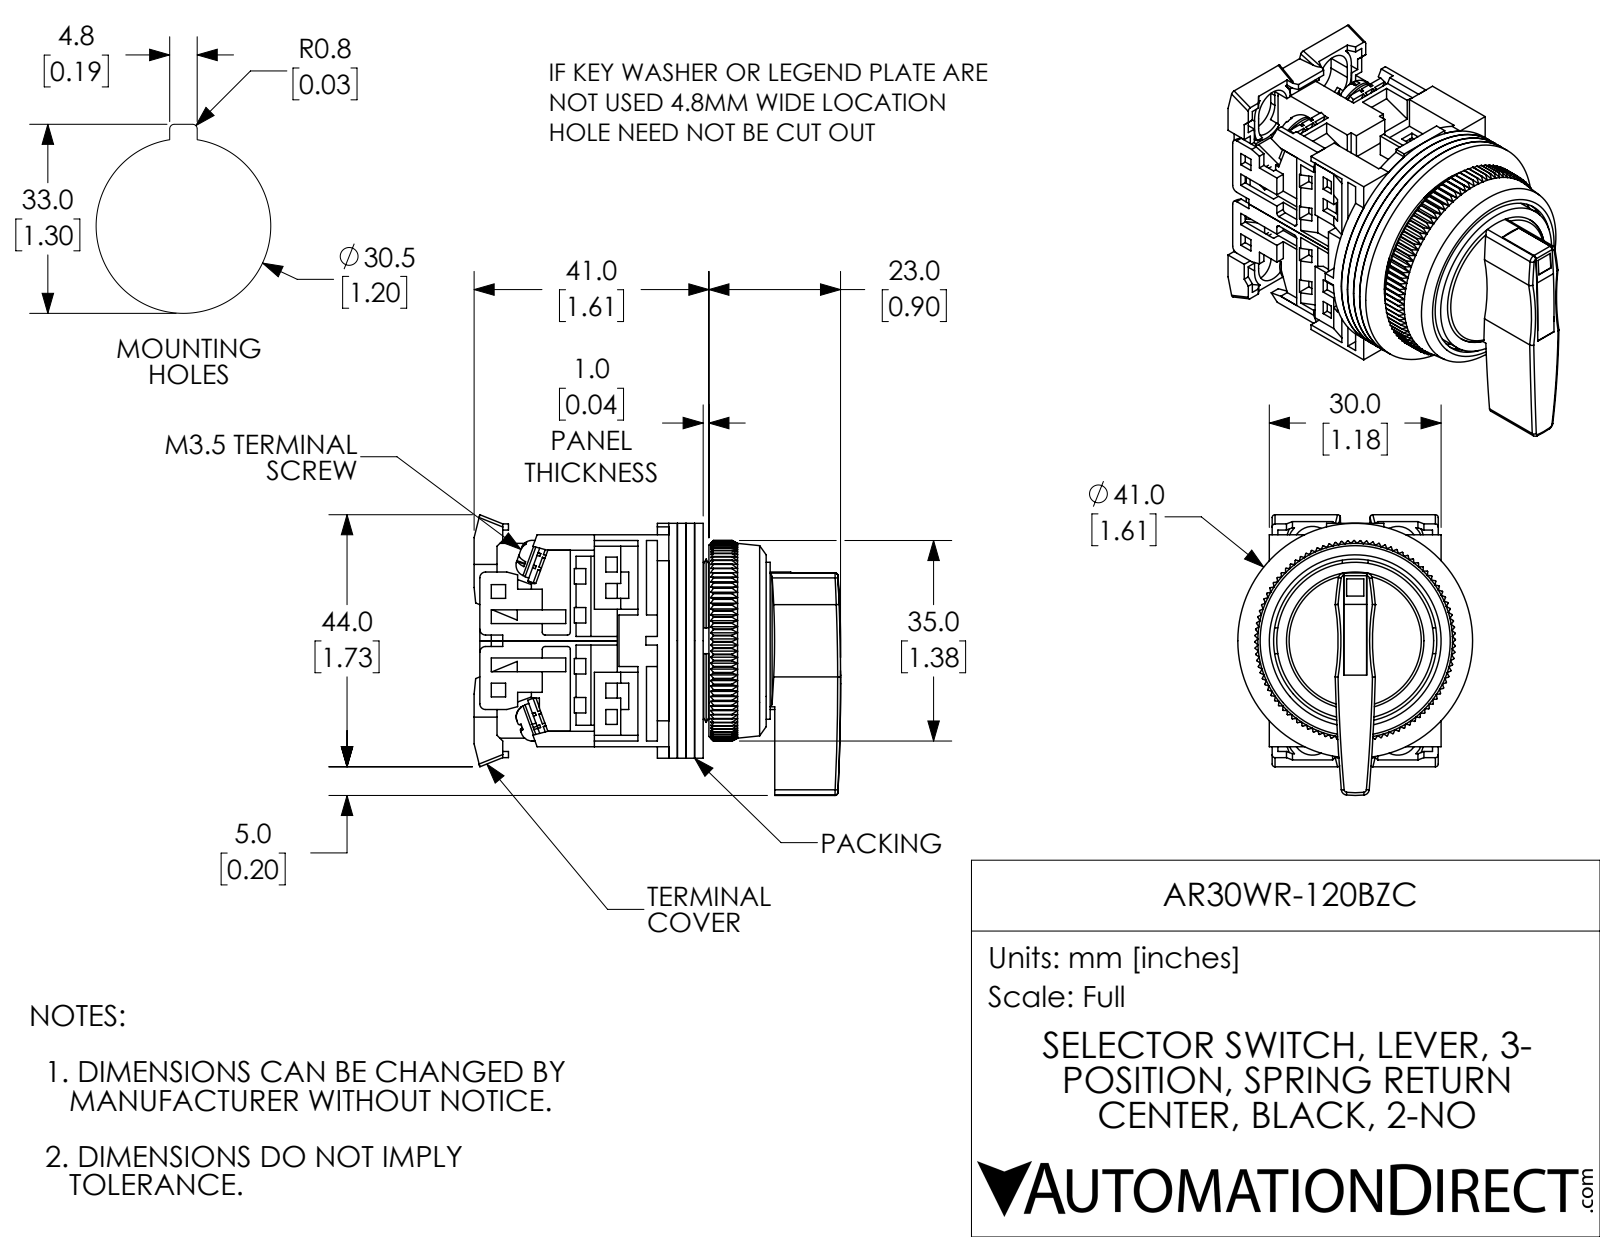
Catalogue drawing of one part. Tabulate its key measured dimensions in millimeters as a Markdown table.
| quantity | value |
| --- | --- |
| part name | AR30WR-120BZC |
| STEP written by | SolidWorks 2017 (AUTOMOTIVE_DESIGN) |
| units | millimeters |
| bodies | 26 solids, 1818 faces (1288 planar, 287 cylindrical, 243 other) |
| overall size | 64 × 49 × 41 |
| volume | 38 230 mm³ |
| surface area | 40 570 mm² |
| round holes (diameter × count) | 3.5 × 8, 3.6 × 4, 3 × 1, 8 × 1, 12 × 1, 12.2 × 1, 13 × 1, 20.8 × 1, 24 × 1, 28.5 × 1, 30 × 1, 31.8 × 1 |
| round bosses / shafts (diameter × count) | 6.6 × 4, 3.5 × 4, 41 × 1, 29.2 × 1, 27.4 × 1, 20 × 1, 18 × 1, 17 × 1 |
| partial cylindrical surfaces (radius × count) | 1.5 × 16, 0.5 × 13, 1 × 8, 3.5 × 4, 4.5 × 4, 3 × 2, 40 × 2, 41.6 × 2 |
| main face-to-face distances | 1.5, 3, 4.5, 1, 2, 36, 5, 34.5, 13, 5.4 |
| hole center spacings | 14.7, 15.5 |
